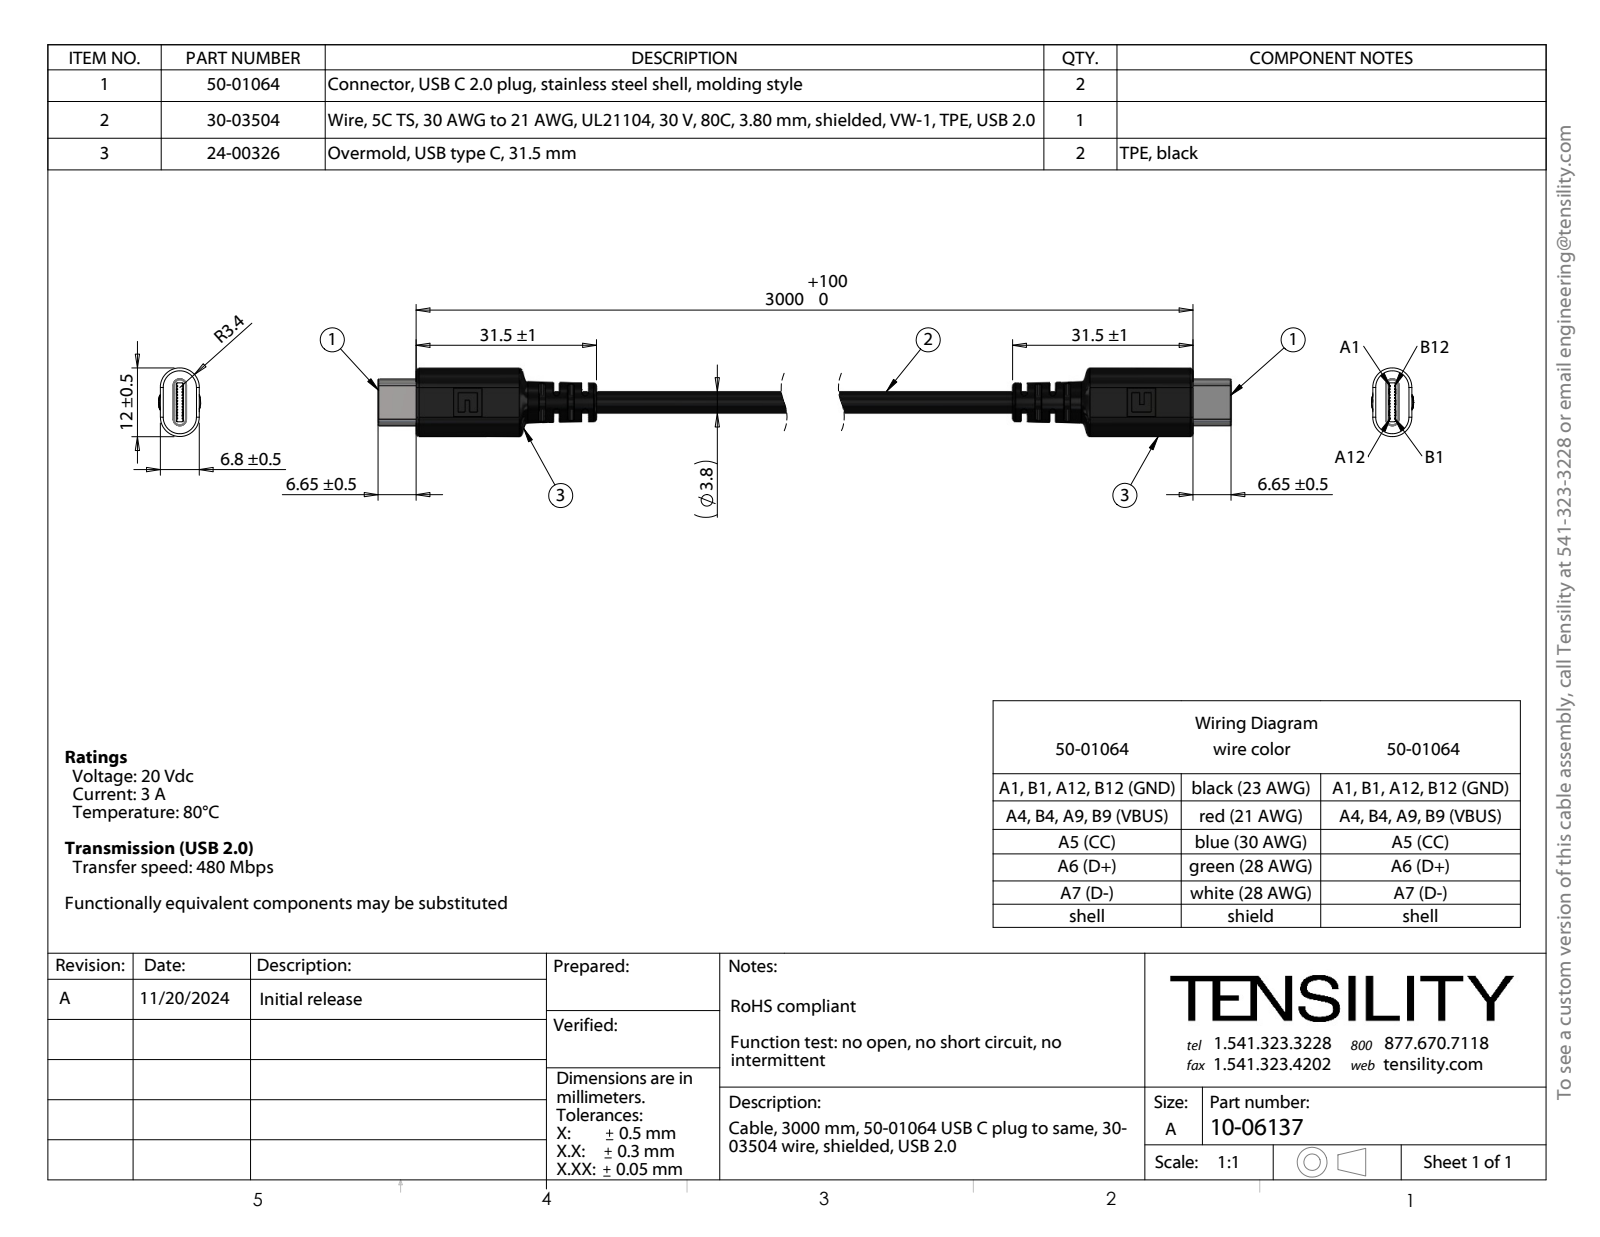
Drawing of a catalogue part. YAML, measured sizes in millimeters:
part_name: "30-03504_blunt cut; 24-00326; 50-01064_Hidden emarker; 10-06137"
step_written_by: "SolidWorks 2021 (CONFIG_CONTROL_DESIGN)"
units: millimeters
bodies: {solids: 55, faces: 1076, planar: 496, cylindrical: 352, other: 228}
overall_size: [206.3, 12, 7.38]
volume: 5080
surface_area: 20593
round_holes:
  - {diameter: 2.73, count: 1}
  - {diameter: 2.76, count: 1}
  - {diameter: 2.98, count: 1}
round_bosses_or_shafts:
  - {diameter: 0.83, count: 2}
  - {diameter: 3.8, count: 1}
  - {diameter: 2.96, count: 1}
  - {diameter: 2.75, count: 1}
  - {diameter: 1.2, count: 1}
  - {diameter: 1, count: 1}
  - {diameter: 0.55, count: 1}
partial_cylinders:
  - {radius: 0.5, count: 20}
  - {radius: 0.1, count: 4}
  - {radius: 0.15, count: 4}
  - {radius: 0.25, count: 4}
  - {radius: 0.6, count: 2}
  - {radius: 1.18, count: 2}
  - {radius: 3.4, count: 2}
face_to_face_distances: [6.8, 2.5, 4.57, 2.23, 2.35, 0.65, 1.7, 2.22, 4.58, 1]
hole_center_spacings: [0.43, 0.33, 0.32, 0.49, 0.59, 0.42, 0.56, 0.88]
